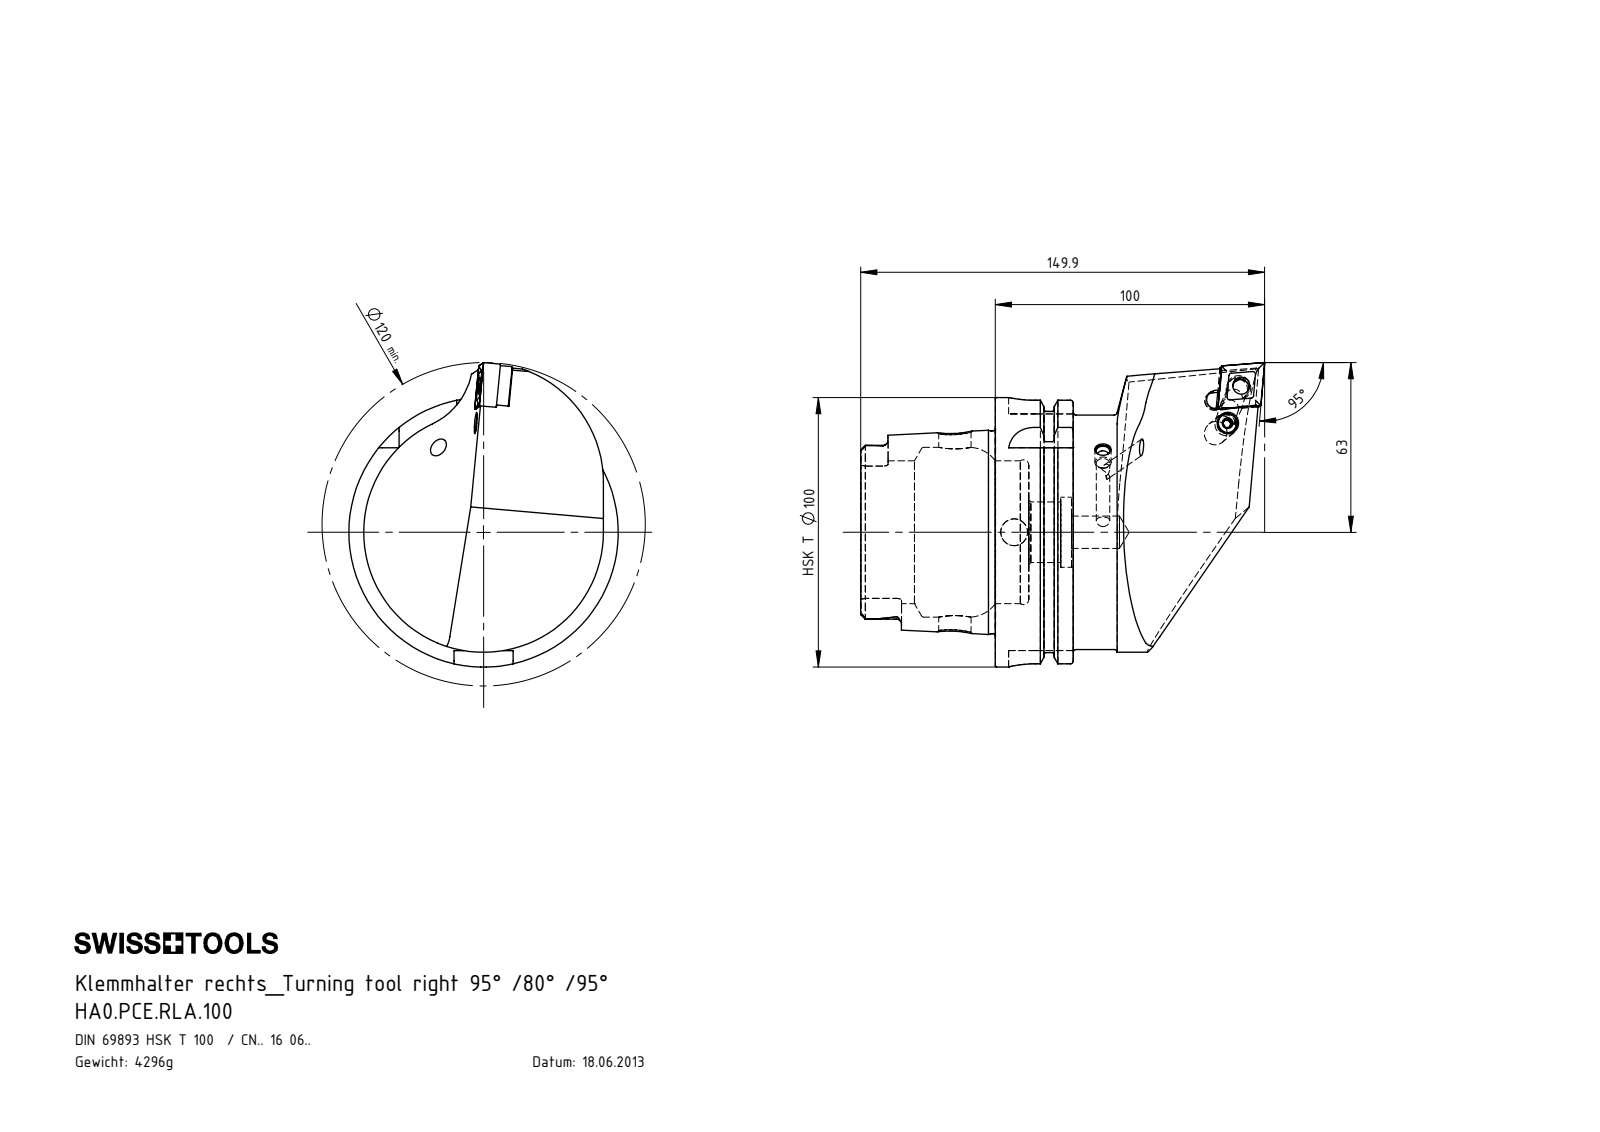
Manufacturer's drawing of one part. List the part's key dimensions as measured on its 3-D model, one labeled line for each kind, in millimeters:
Part name (STEP PRODUCT): HA0.PCE.RLA.100; WCE-ER3.101.000_A; WCE-ER4.101.020_A; KVT_MB_600_060 (+3 more)
STEP written by: SolidWorks 2012 (CONFIG_CONTROL_DESIGN)
Units: millimetres
Bodies: 7 solids, 368 faces (115 planar, 103 cylindrical, 150 other)
Overall size (bounding box): 149.9 × 113 × 100
Volume: 546 076 mm³ · Surface area: 72 119 mm²
Round holes (diameter × count): ⌀5 ×2, ⌀12 ×2, ⌀6.35 ×1, ⌀7 ×1, ⌀8.05 ×1, ⌀8.4 ×1, ⌀10 ×1, ⌀22.5 ×1, ⌀26 ×1, ⌀53 ×1, ⌀63 ×1
Round bosses / shafts (diameter × count): ⌀6 ×2, ⌀100 ×1, ⌀91.95 ×1, ⌀87 ×1, ⌀75.26 ×1, ⌀8 ×1, ⌀7.9 ×1, ⌀6.4 ×1
Partial cylindrical surfaces — rounded edges, fillets, slot ends (radius × count): R1.9 ×6, R0.4 ×4, R1.5 ×4, R10 ×4, R3.5 ×3, R0.3 ×2, R4.83 ×2, R4.88 ×2
Main face-to-face distances: 12.45, 28.95, 16.5, 49.9, 62.35, 78.85, 87.8, 78.2, 28.3, 15.85
Hole centre spacings: 14.75, 14.99
